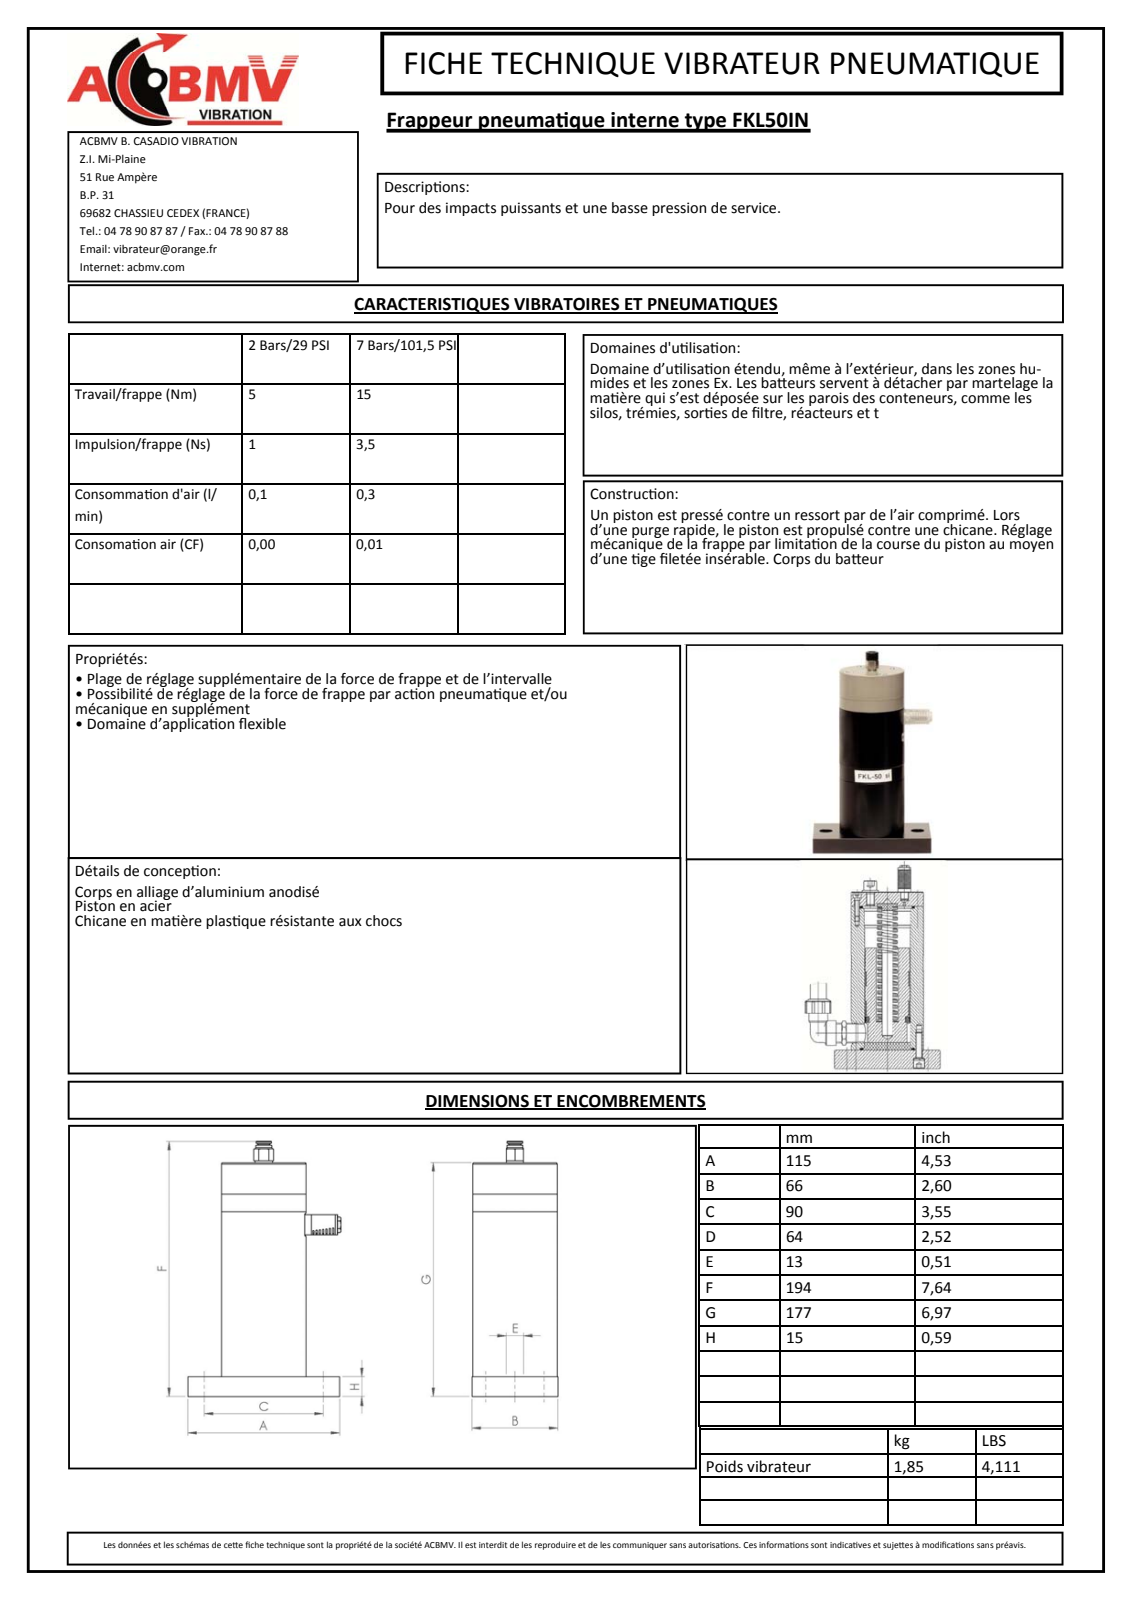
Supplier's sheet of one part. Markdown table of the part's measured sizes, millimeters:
| quantity | value |
| --- | --- |
| part name | 4050-00; 94050-50; 94050-40; 94050-30 (+8 more) |
| STEP written by | Autodesk Inventor 2009 (CONFIG_CONTROL_DESIGN) |
| units | millimeters |
| bodies | 39 solids, 550 faces (236 planar, 119 cylindrical, 195 other) |
| overall size | 193.12 × 116 × 65 |
| volume | 552 955 mm³ |
| surface area | 169 045 mm² |
| round holes (diameter × count) | 6.4 × 10, 6 × 1, 8.3 × 1, 10.5 × 1, 15 × 1, 19 × 1, 19.5 × 1, 27 × 1, 32 × 1, 33 × 1, 35.8 × 1, 36 × 1 |
| round bosses / shafts (diameter × count) | 10.2 × 10, 10 × 10, 6 × 10, 64 × 1, 58 × 1, 39 × 1, 38 × 1, 35.3 × 1 |
| partial cylindrical surfaces (radius × count) | 6.75 × 1 |
| main face-to-face distances | 15, 125, 13, 140, 8, 153, 138, 177, 162, 37 |
| hole center spacings | 28.5, 24.54, 25, 35.36, 51.45, 8.42, 10.99, 13.6 |
